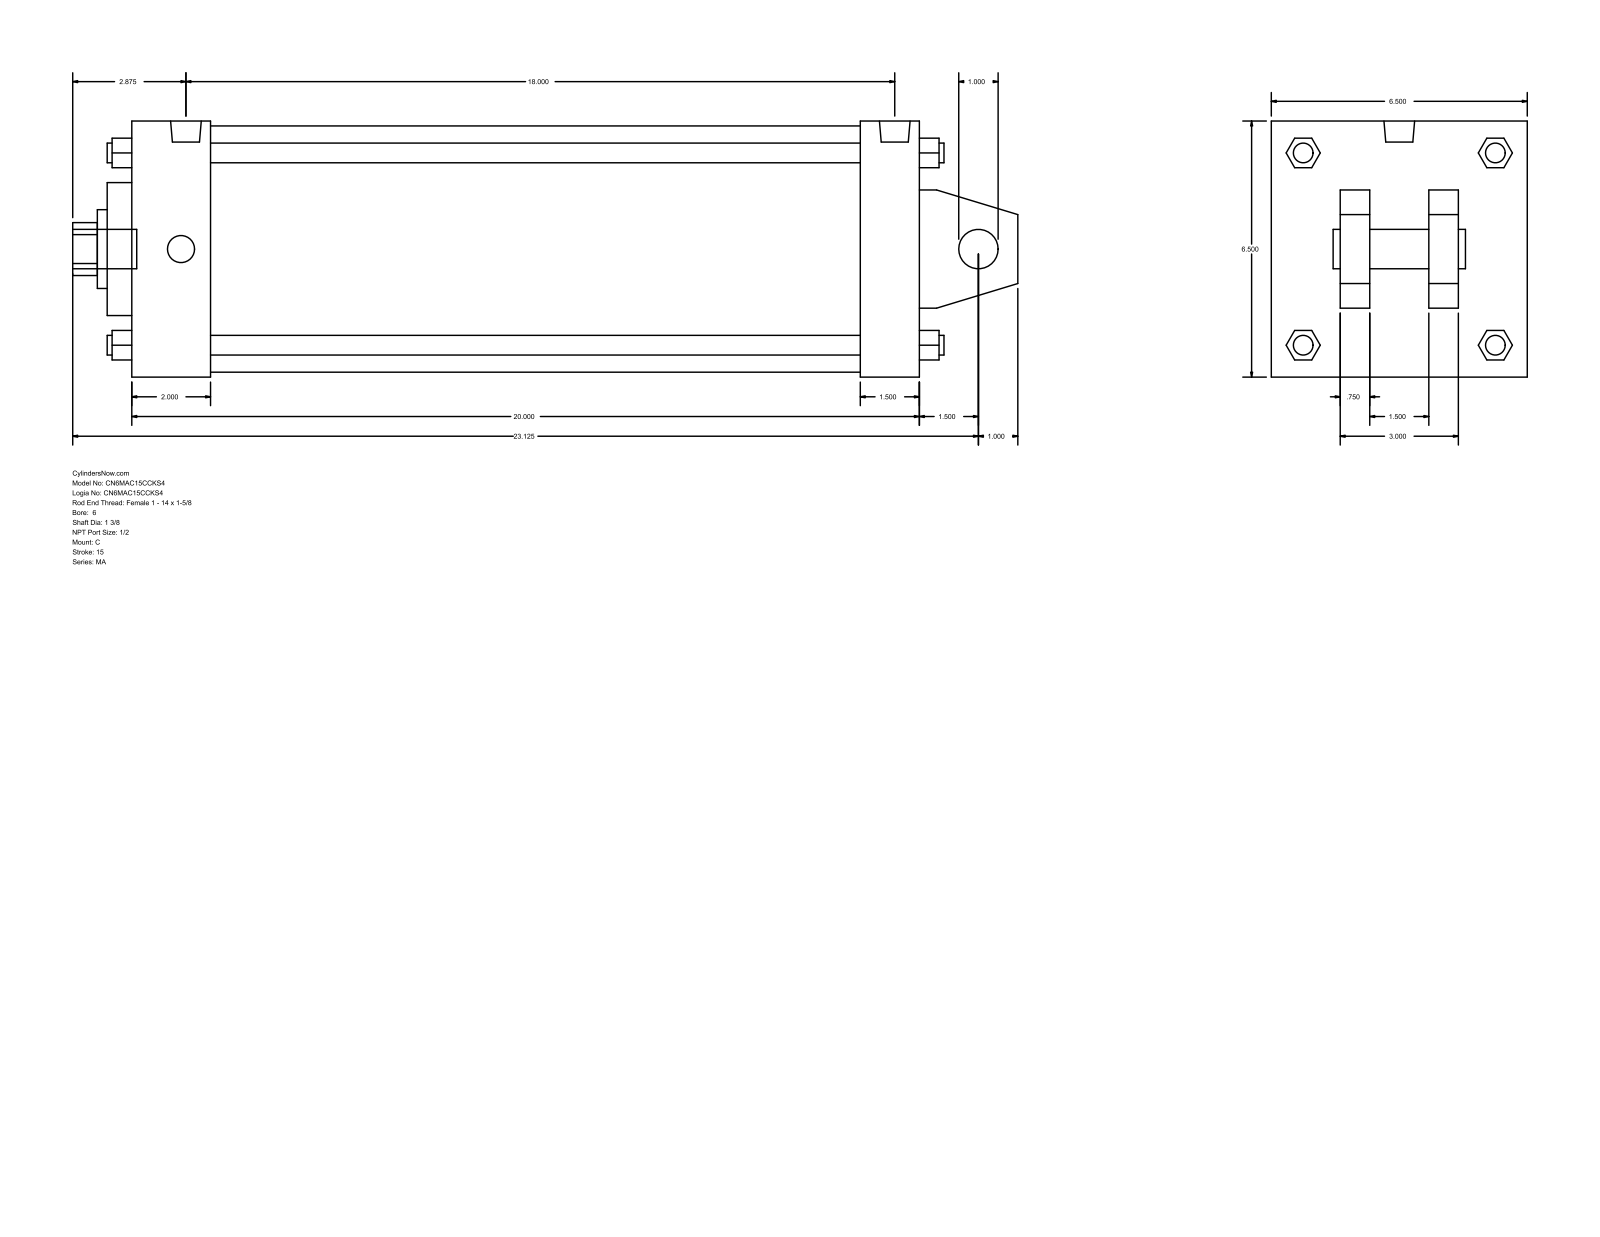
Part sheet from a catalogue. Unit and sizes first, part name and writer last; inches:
Units: inches
Overall size (bounding box): 24 × 6.5 × 6.5
Round holes (diameter × count): ⌀1 ×1, ⌀1.375 ×1, ⌀2 ×1, ⌀3.375 ×1, ⌀6.25 ×1
Round bosses / shafts (diameter × count): ⌀0.687 ×4, ⌀0.5 ×4, ⌀0.778 ×2, ⌀1 ×1
Partial cylindrical surfaces — rounded edges, fillets, slot ends (radius × count): R0.672 ×1
Main face-to-face distances: 6.5, 20, 1.5, 0.75, 2.5, 4, 2, 1.75, 4.75, 18.5
Bodies: 0 solids, 141 faces (109 planar, 32 cylindrical, 0 other)
Part name (STEP PRODUCT): MA_C__0600_1.375
STEP written by: GSSL Pune (CONFIG_CONTROL_DESIGN)
